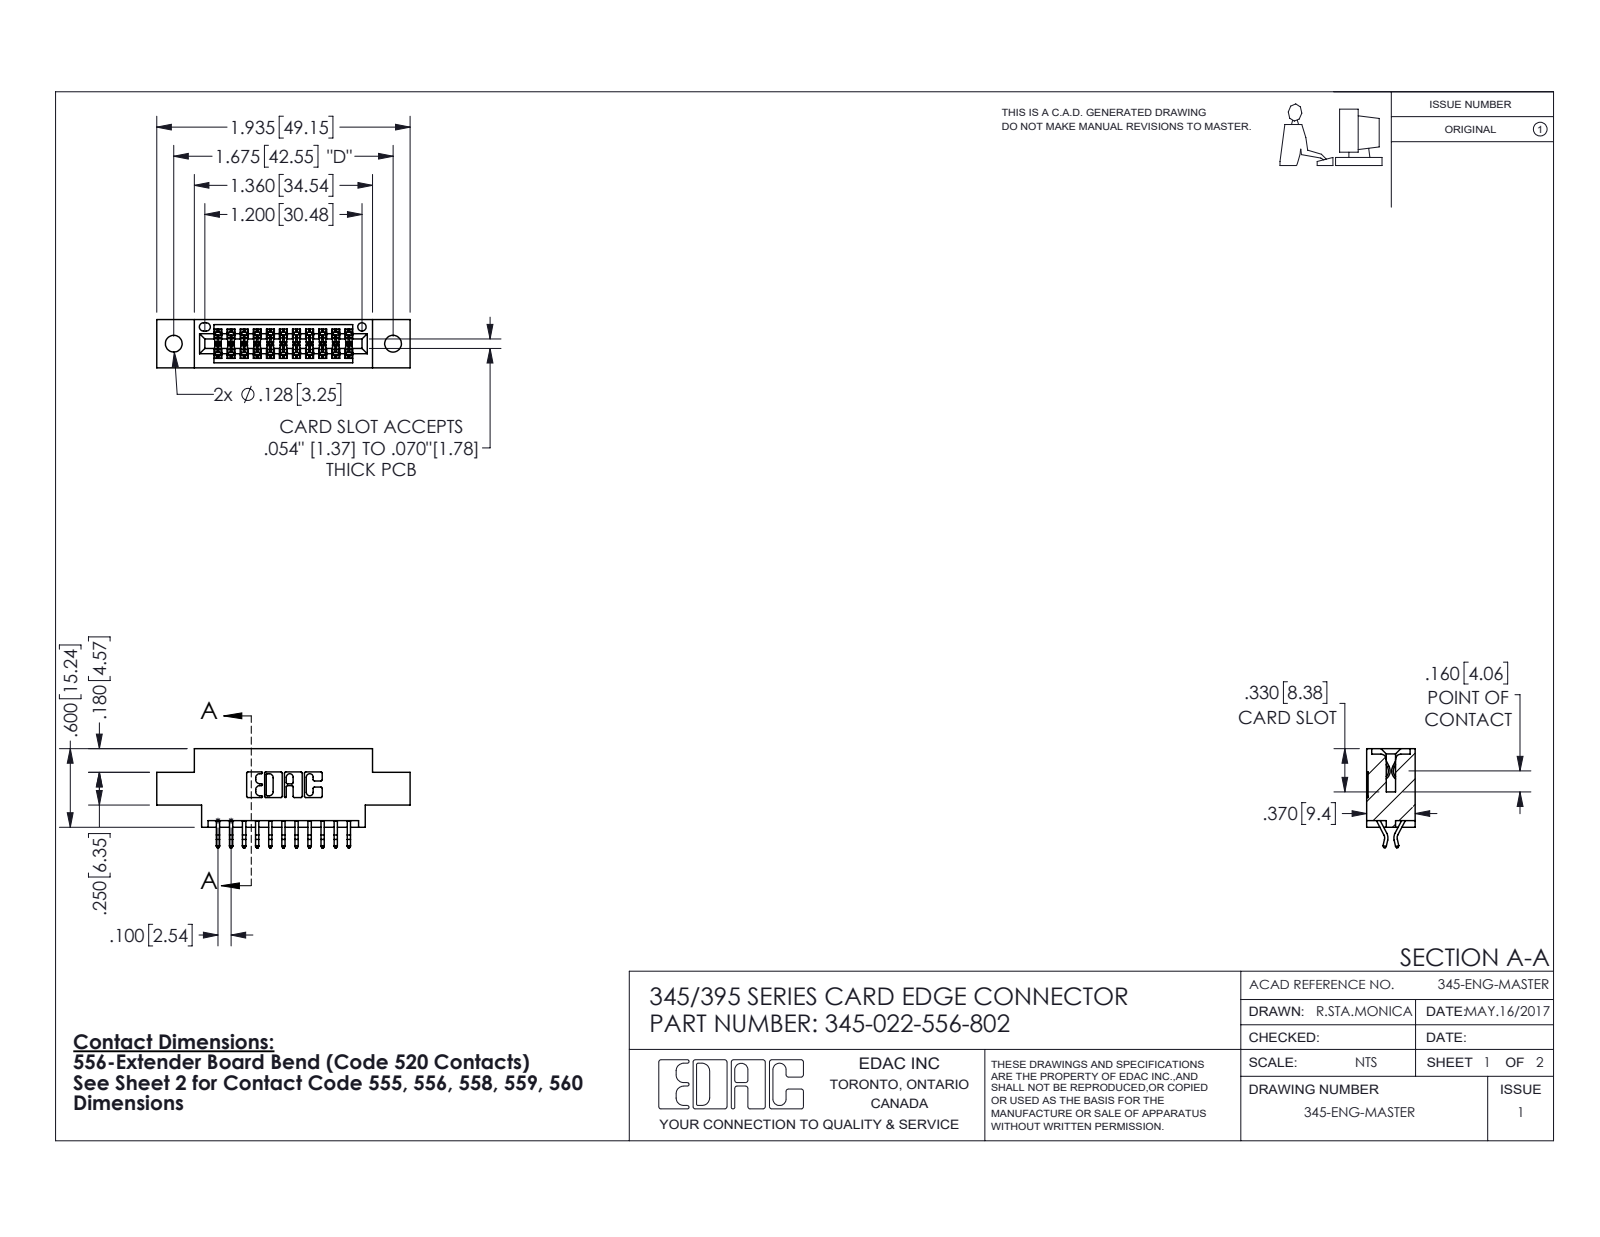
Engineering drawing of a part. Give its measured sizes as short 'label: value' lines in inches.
name: 345-292-001_556 Tail; 345-022-556-802; 345 Part_0.170 Offset - 0.128 Dia
written by: SolidWorks 2016 (CONFIG_CONTROL_DESIGN)
unit: in
bodies: 23 solids, 1362 faces (898 planar, 464 cylindrical, 0 other)
size: 1.935 × 0.757 × 0.37
volume: 0.265 in³; area: 8.773 in²
holes: 2× ⌀0.128, 1× ⌀0.064
rounds: 33× R0.006, 22× R0.01, 6× R0.007, 6× R0.031, 3× R0.026, 2× R0.01, 2× R0.014, 2× R0.019
face distances: 0.37, 0.298, 0.072, 0.2, 0.025, 0.098, 0.272, 0.1, 0.225, 0.6
hole spacings: 0.27, 1.443, 1.675
